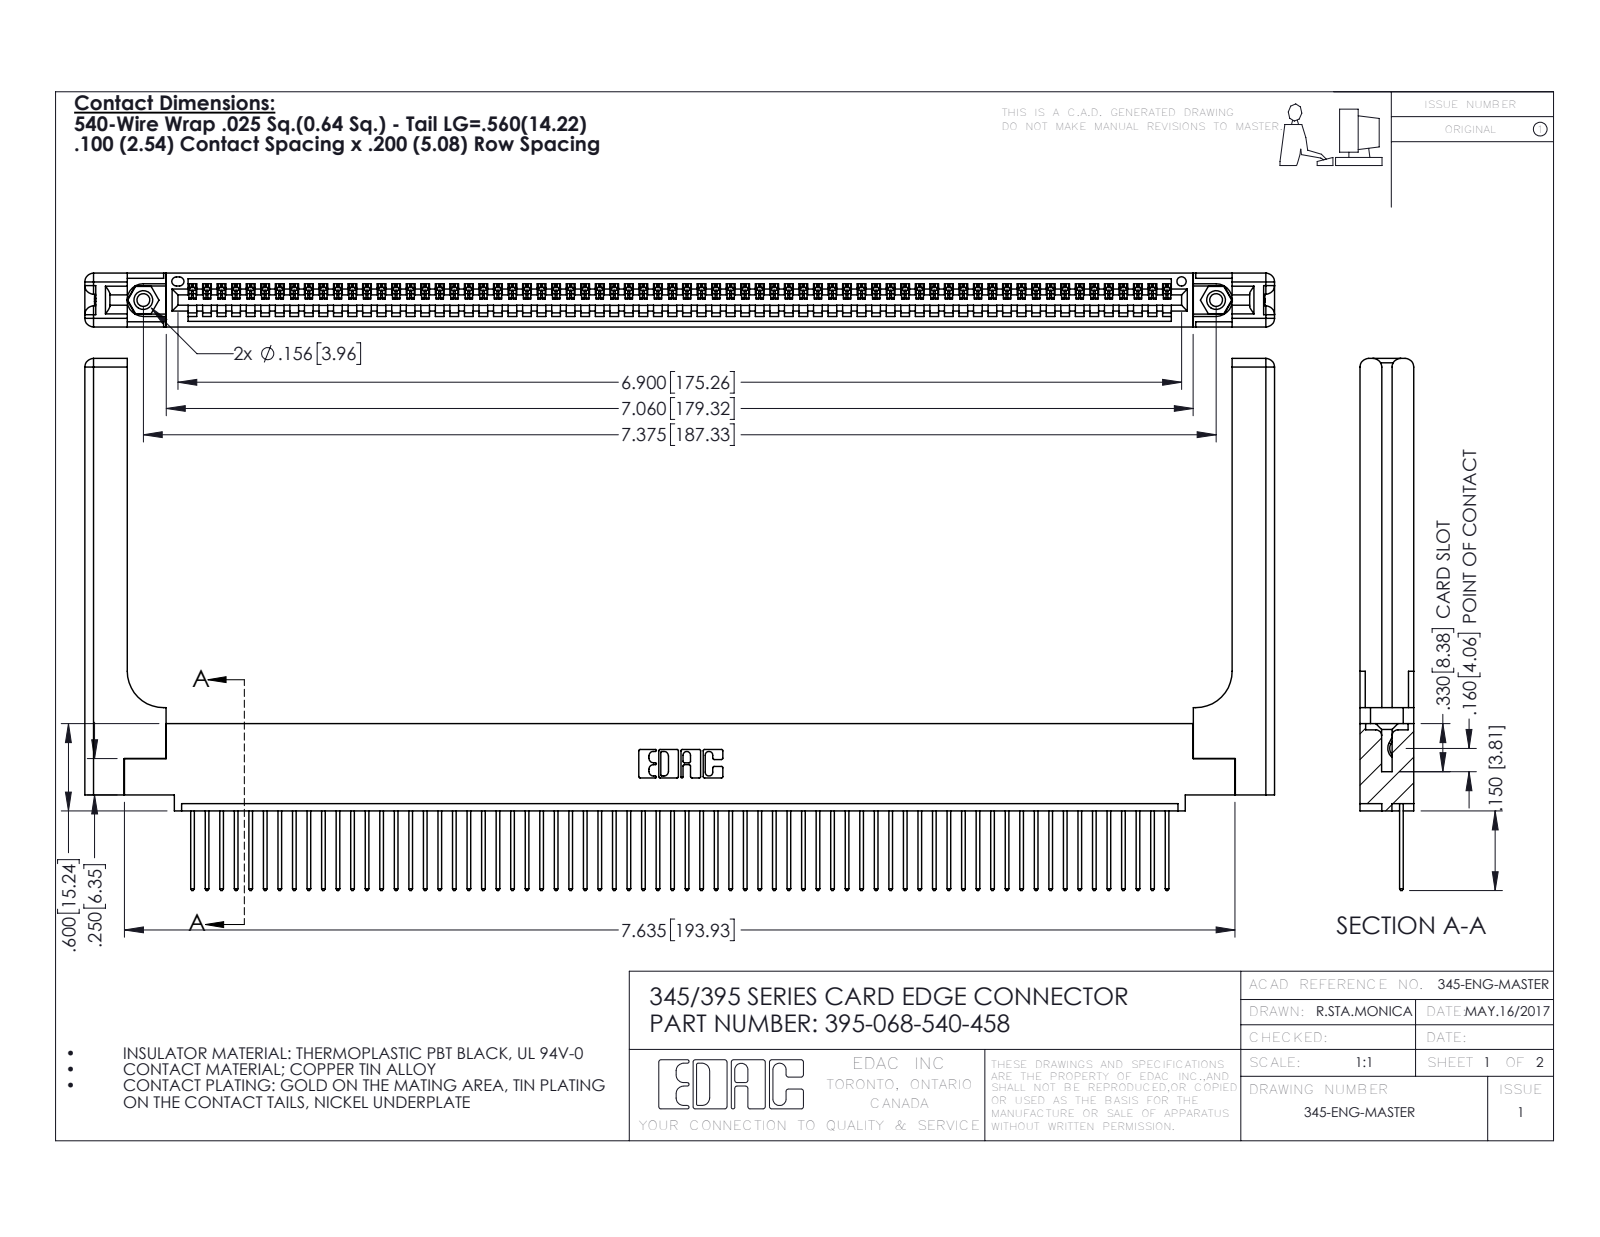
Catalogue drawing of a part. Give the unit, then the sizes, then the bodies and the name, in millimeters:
Units: millimetres
Overall size (bounding box): 207.7 × 92.9 × 9.4
Round holes (diameter × count): ⌀2.3 ×2, ⌀3.2 ×2, ⌀4 ×2, ⌀1.6 ×1
Round bosses / shafts (diameter × count): ⌀3.9 ×2
Partial cylindrical surfaces — rounded edges, fillets, slot ends (radius × count): R0.2 ×136, R0.3 ×136, R0.3 ×22, R1.5 ×16, R0.2 ×6, R0.8 ×6, R0.7 ×3, R0.8 ×2
Main face-to-face distances: 1.8, 7.6, 9.4, 2.5, 6.9, 0.6, 5.1, 5.7, 3.8, 3.8
Hole centre spacings: 6.9, 181.3, 187.3
Volume: 28 460 mm³ · Surface area: 32 940 mm²
Bodies: 73 solids, 4330 faces (2952 planar, 1318 cylindrical, 60 other)
Part name (STEP PRODUCT): 395-068-540-458; 345-220-058_345-220-058; 345-292-001_345-293-140; 345 Part_0.110 Offset - 0.156 Dia-TH (+1 more)
STEP written by: SolidWorks 2016 (CONFIG_CONTROL_DESIGN)
